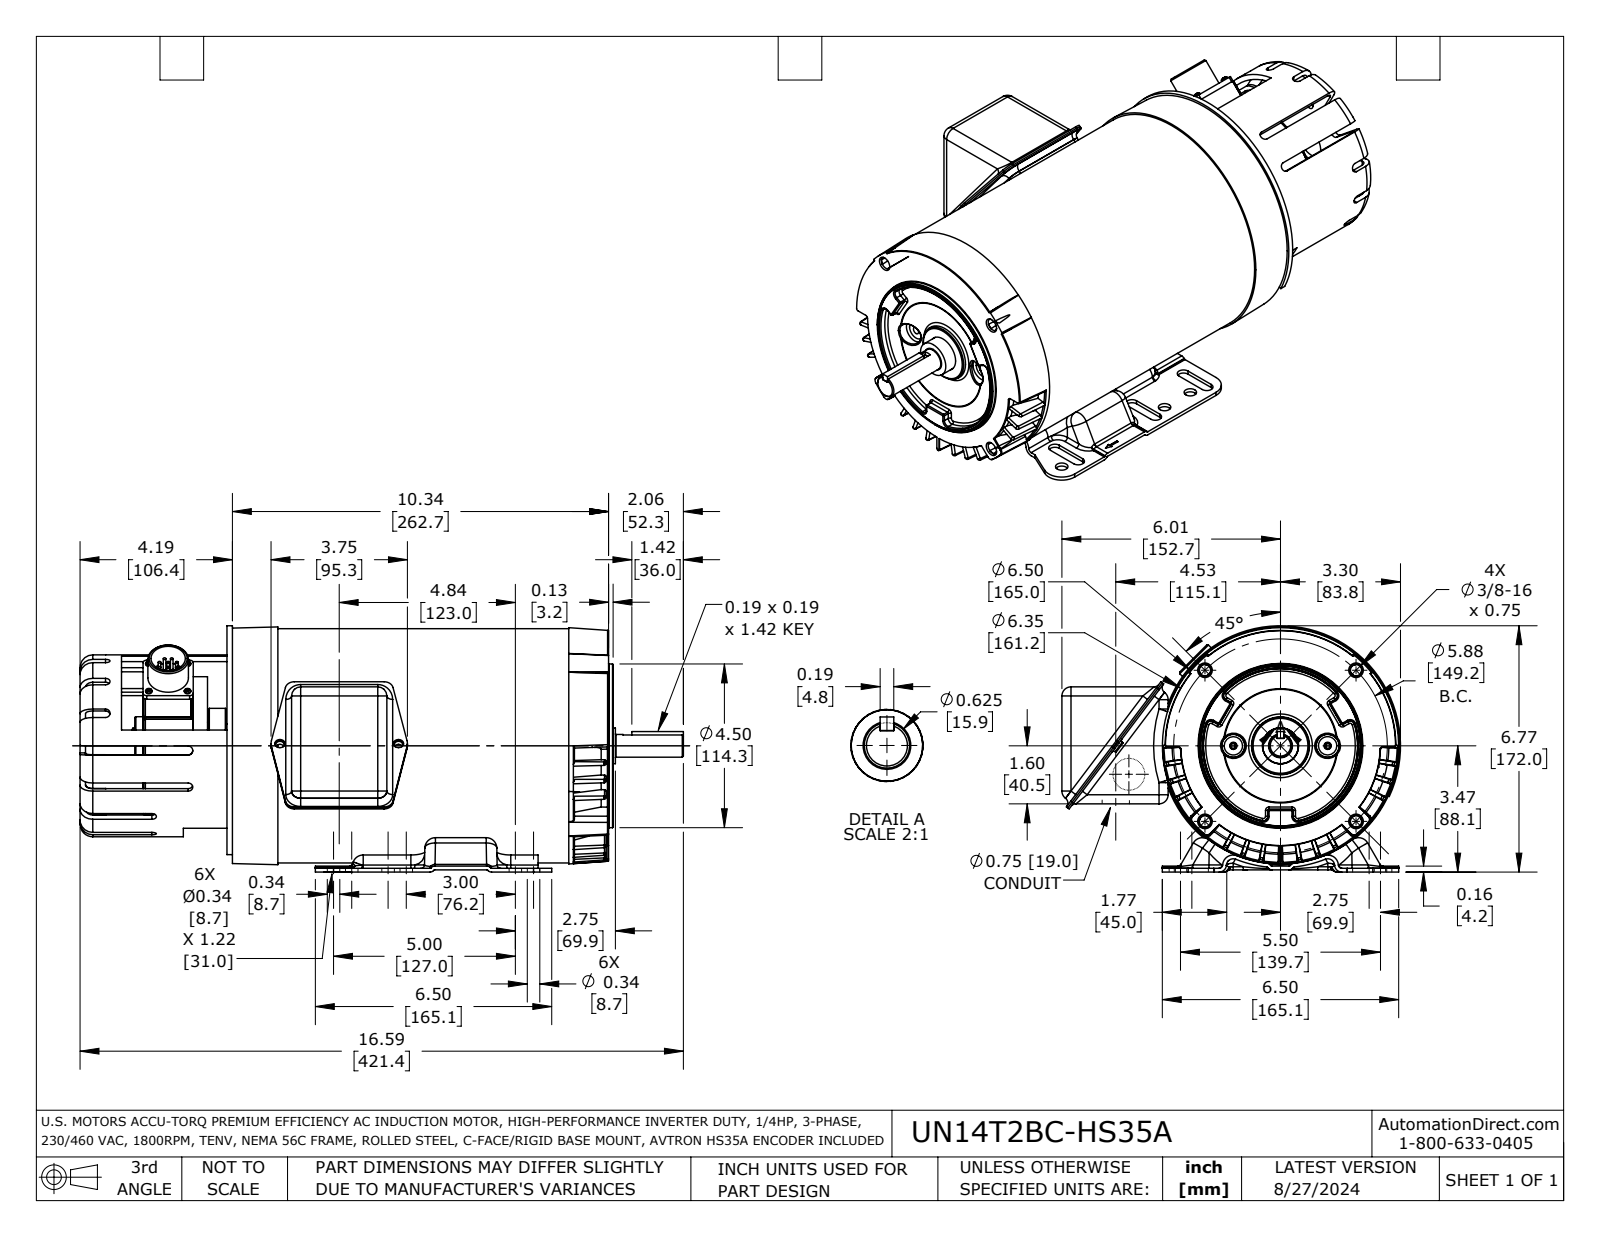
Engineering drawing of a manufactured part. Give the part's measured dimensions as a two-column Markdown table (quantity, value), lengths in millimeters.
| quantity | value |
| --- | --- |
| part name | UN14T2BC-HS35A |
| STEP written by | SolidWorks 2021 (AUTOMOTIVE_DESIGN) |
| units | millimeters |
| bodies | 26 solids, 3051 faces (756 planar, 717 cylindrical, 1578 other) |
| overall size | 421.4 × 236.5 × 172 |
| volume | 1 680 000 mm³ |
| surface area | 752 300 mm² |
| round holes (diameter × count) | 6.4 × 8, 8.7 × 6, 10.2 × 6, 3 × 4, 5.1 × 4, 7.7 × 4, 10.7 × 4, 14 × 4, 3.5 × 3, 2.5 × 2, 4.4 × 2, 5.8 × 2 |
| round bosses / shafts (diameter × count) | 1.8 × 8, 4.4 × 4, 3 × 4, 3.8 × 3, 8.3 × 2, 1.8 × 2, 163.6 × 1, 160.4 × 1 |
| partial cylindrical surfaces (radius × count) | 1.6 × 91, 0.8 × 71, 3.2 × 42, 6.4 × 26, 5.1 × 18, 2.4 × 13, 1.2 × 12, 4.4 × 12 |
| main face-to-face distances | 1.2, 27.4, 34.9, 62.4, 3.8, 102.6, 2.6, 3, 13.5, 1.5 |
| hole center spacings | 53.3, 57, 86.8, 110.5, 137.7, 52.7, 56.7, 56.7 |
